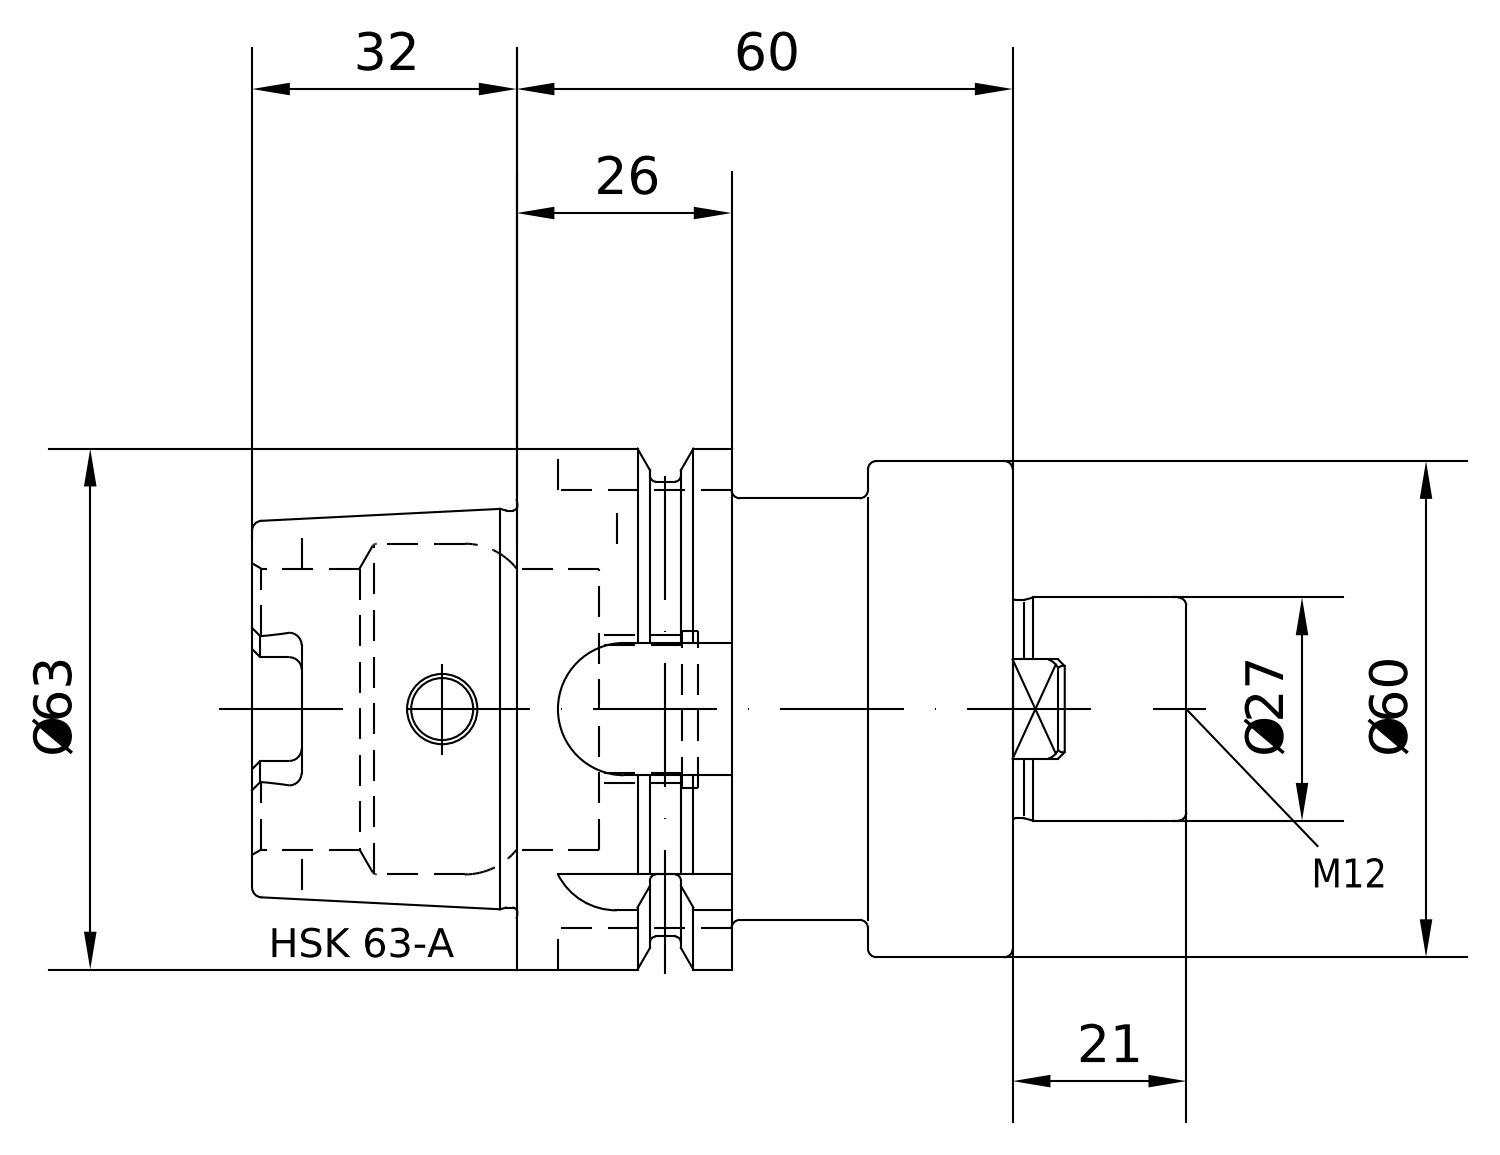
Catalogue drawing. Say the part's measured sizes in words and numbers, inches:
The part is named "A63-050-27". Its 3-D file was written by "PRO/ENGINEER BY PARAMETRIC TECHNOLOGY CORPORATION, 2010430 (CONFIG_CONTROL_DESIGN)". It is 1 solid with 198 faces: 70 planar, 54 cylindrical and 74 other. Overall it measures 4.449 by 2.48 by 2.48 inches. Its volume is 10.73 cubic inches and its surface area 53.09 square inches. Round holes: 1 of diameter 0.295, 1 of diameter 0.394, 1 of diameter 0.402, 1 of diameter 0.472, 1 of diameter 0.666, 1 of diameter 0.721, 1 of diameter 0.735, 1 of diameter 1.339, 1 of diameter 1.575. Round bosses or shafts: 1 of diameter 2.48, 1 of diameter 2.362, 1 of diameter 2.165, 1 of diameter 2.008, 1 of diameter 1.891, 1 of diameter 1.063, 1 of diameter 0.709. Partial cylindrical surfaces (rounded edges, fillets, slot ends): 6 of radius 0.059, 4 of radius 0.118, 1 of radius 0.315, 1 of radius 0.316, 1 of radius 0.355. The main face-to-face distances are 2.362, 1.024, 1.339, 0.394, 2.165, 0.63, 1.969, 3.189, 1.654, 1.673.
